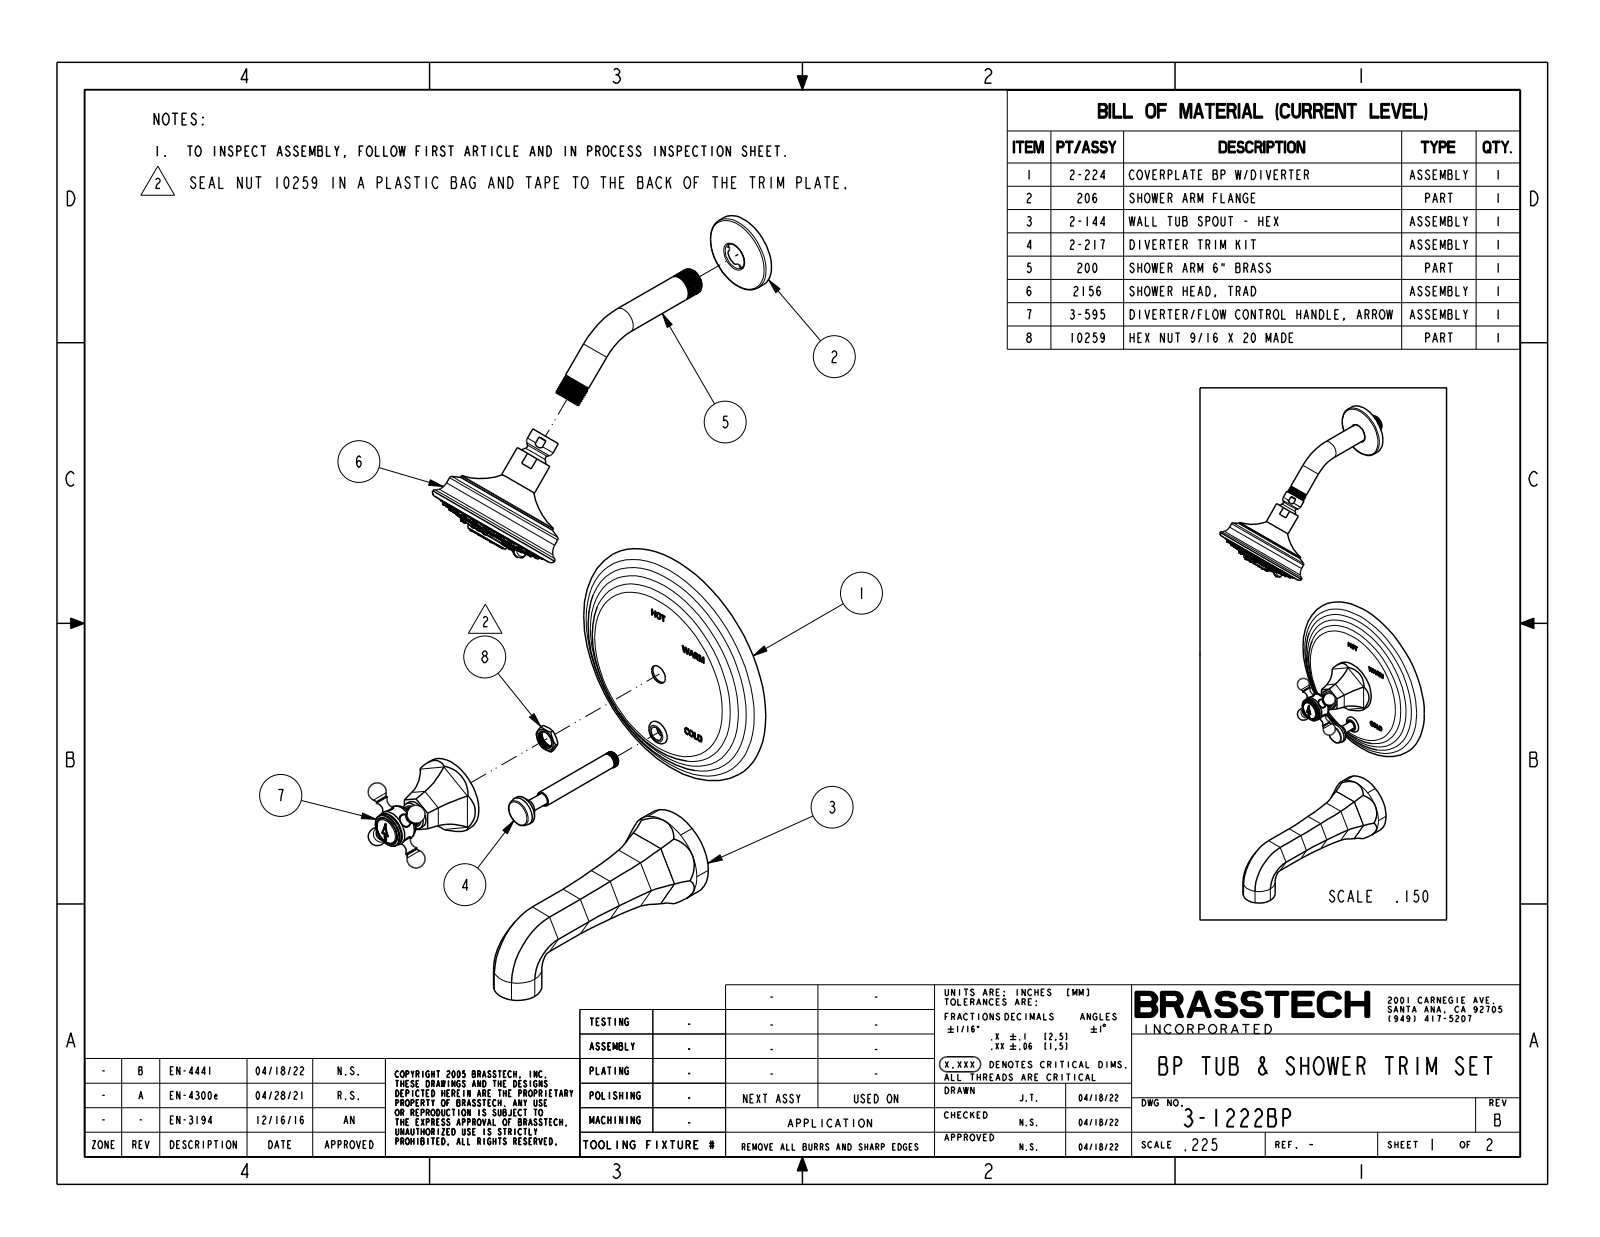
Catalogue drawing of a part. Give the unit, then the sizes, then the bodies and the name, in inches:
Units: inches
Overall size (bounding box): 23.835 × 8.25 × 7.75
Round holes (diameter × count): ⌀0.059 ×8, ⌀0.41 ×2, ⌀0.855 ×1, ⌀0.925 ×1
Round bosses / shafts (diameter × count): ⌀0.142 ×39, ⌀0.165 ×23, ⌀0.813 ×2, ⌀0.392 ×2, ⌀3.81 ×1, ⌀3.724 ×1, ⌀3.24 ×1, ⌀2.8 ×1
Partial cylindrical surfaces — rounded edges, fillets, slot ends (radius × count): R0.079 ×8, R1.541 ×6, R2.125 ×6, R0.015 ×2, R0.02 ×2, R1 ×2, R1.02 ×2, R0.02 ×1
Main face-to-face distances: 0.754, 1.299, 0.995, 2.294, 0.063, 0.118, 0.181, 1.938, 1.184, 2.401
Hole centre spacings: 0.579, 0.443, 1.069, 0.818, 0.819, 1.157, 0.443, 1.069
Volume: 71.31 in³ · Surface area: 247.9 in²
Bodies: 3 solids, 1458 faces (276 planar, 251 cylindrical, 931 other)
Part name (STEP PRODUCT): 3-1222BP
STEP written by: CREO PARAMETRIC BY PTC INC, 2018400 (CONFIG_CONTROL_DESIGN)
